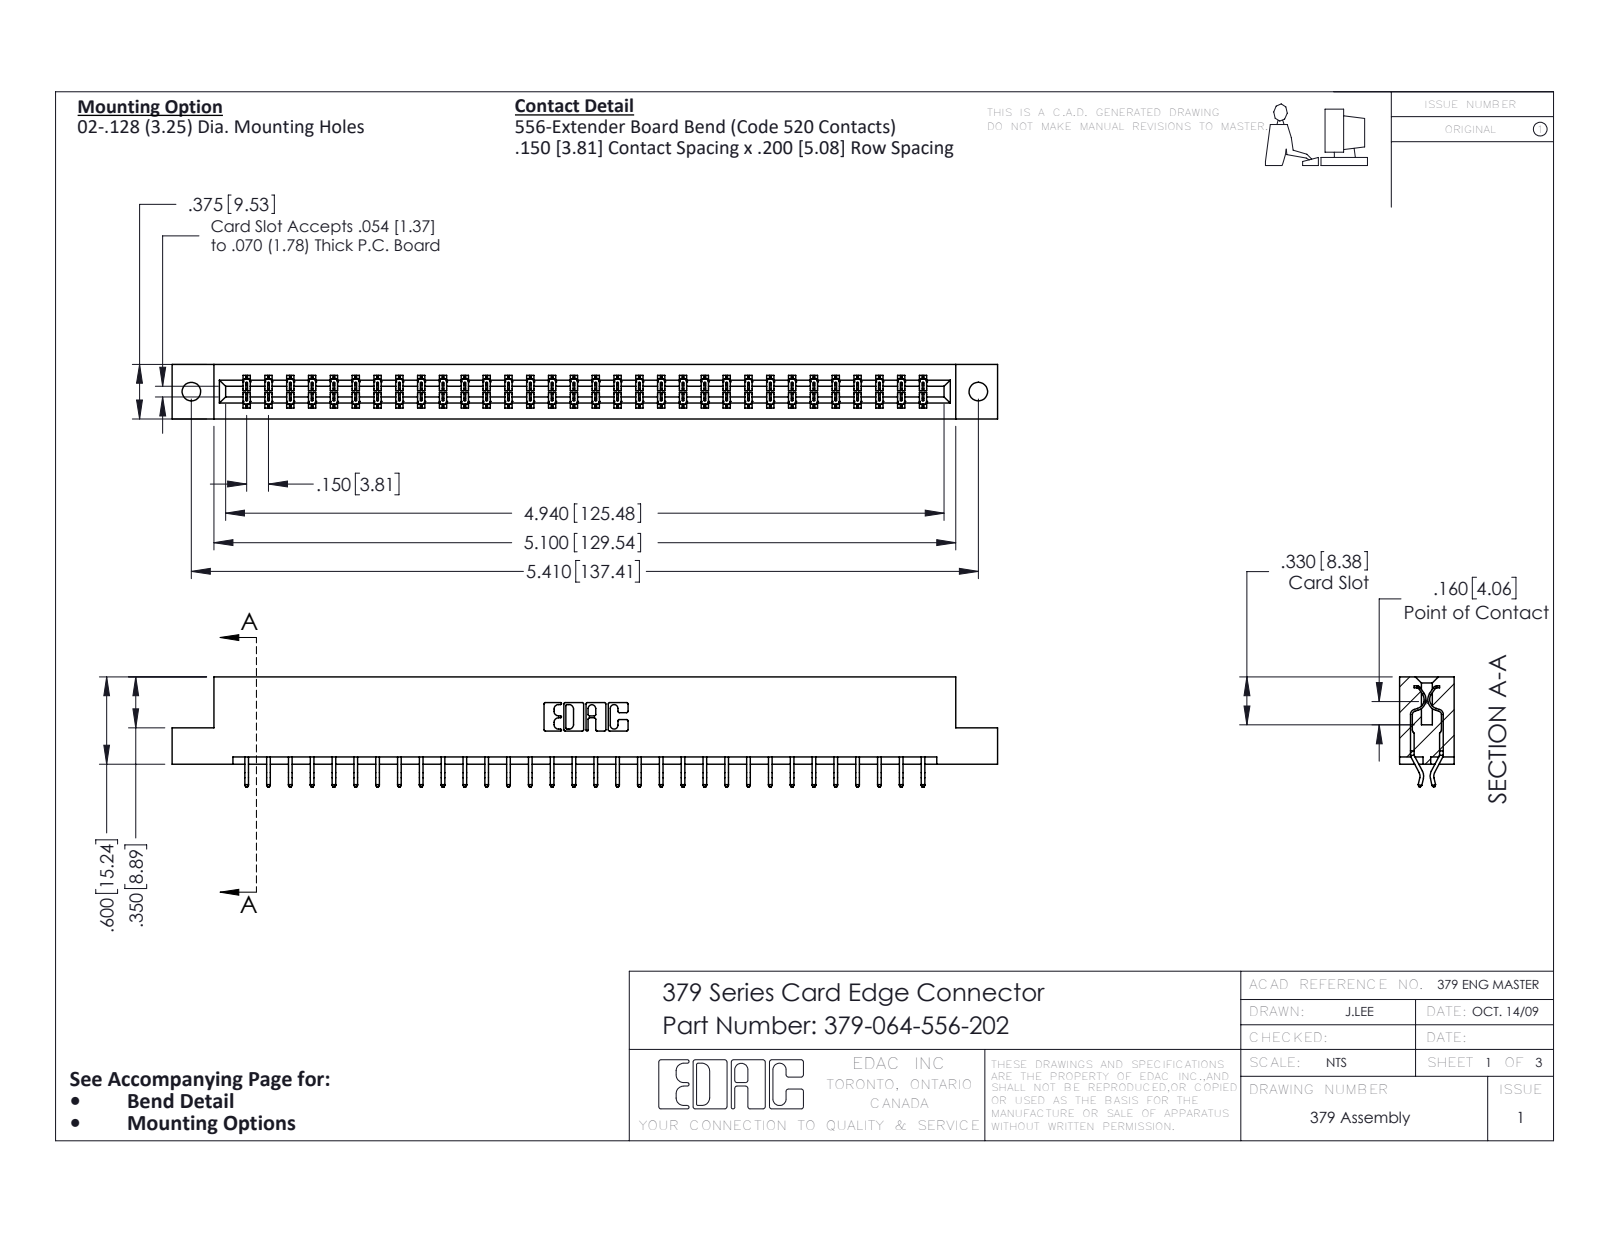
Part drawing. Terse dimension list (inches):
name: 379 Part_Flush - .128 Dia; 379-064-556-202; 345-292-001_556 Tail
written by: SolidWorks 2016 (CONFIG_CONTROL_DESIGN)
unit: in
bodies: 65 solids, 3826 faces (2630 planar, 1196 cylindrical, 0 other)
size: 5.675 × 0.757 × 0.375
volume: 0.927 in³; area: 25.78 in²
holes: 2× ⌀0.128
rounds: 96× R0.006, 22× R0.01, 6× R0.007, 6× R0.031, 3× R0.026, 2× R0.01, 2× R0.014, 2× R0.022
face distances: 0.3, 0.075, 0.375, 0.2, 0.225, 0.1, 0.15, 0.076, 0.55, 0.025
hole spacings: 5.41
